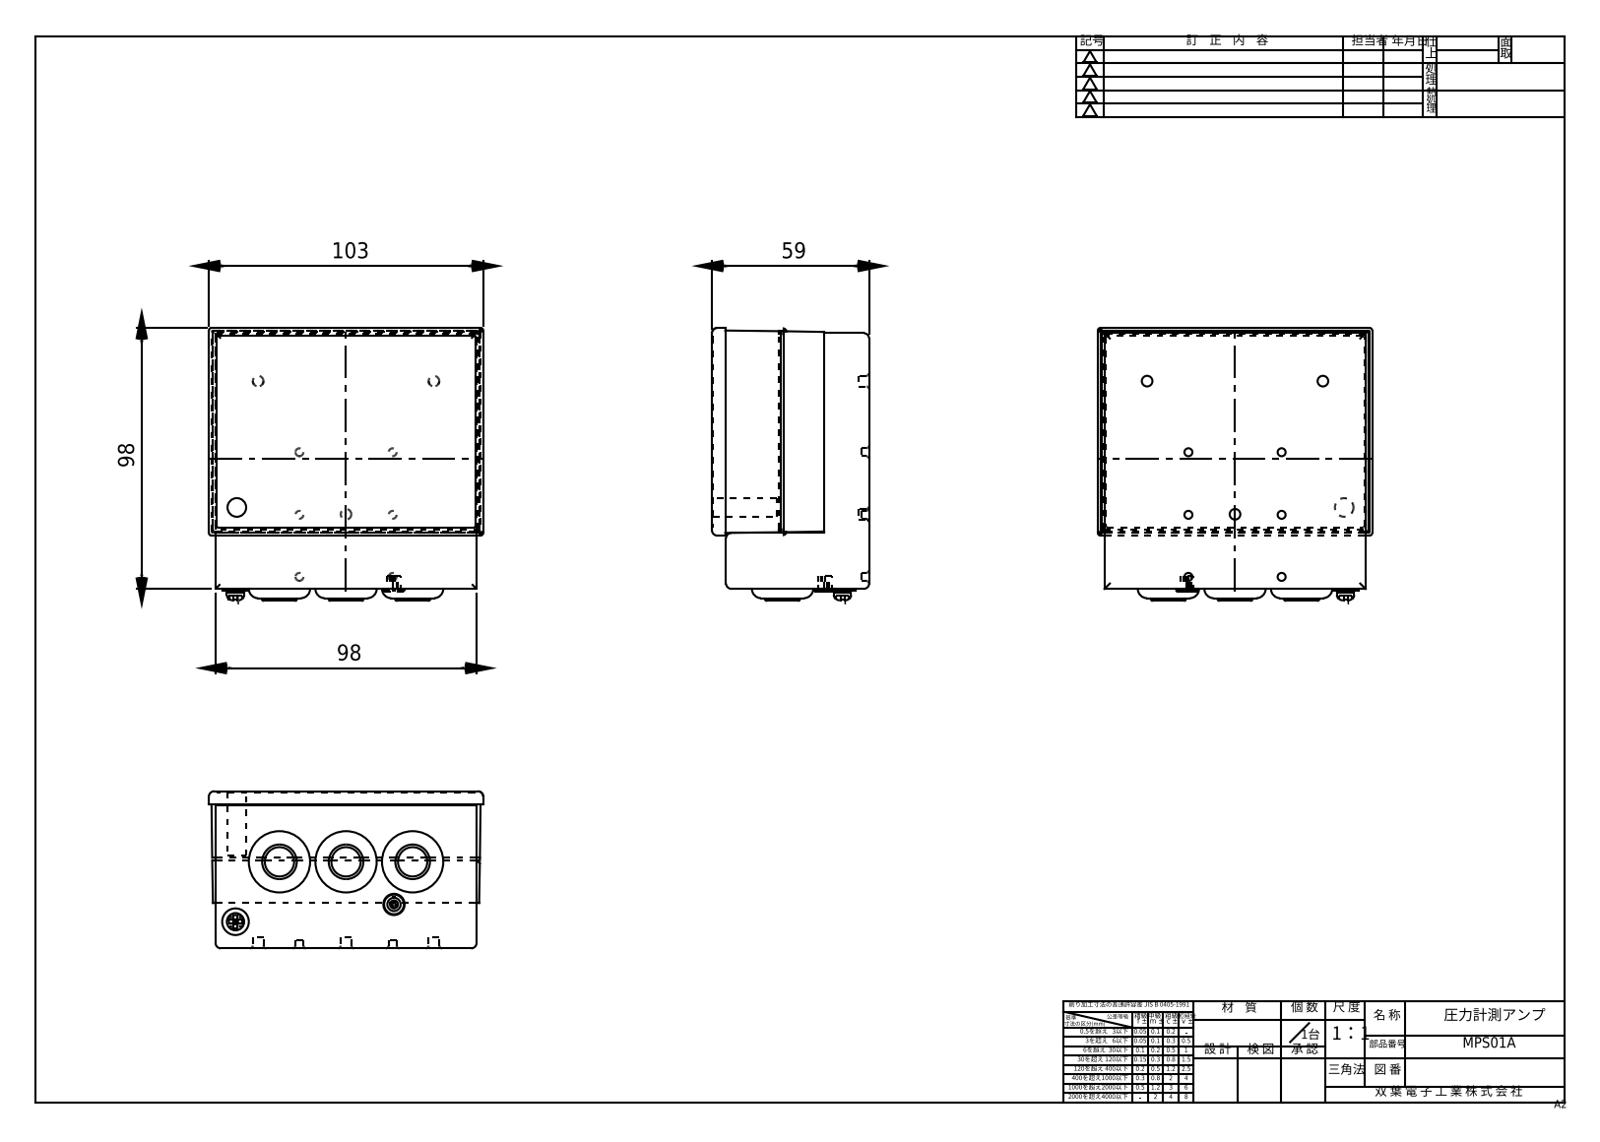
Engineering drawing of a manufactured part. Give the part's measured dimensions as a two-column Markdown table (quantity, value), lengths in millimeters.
| quantity | value |
| --- | --- |
| STEP written by | XStep 1.0 (automotive_design) |
| units | millimeters |
| bodies | 1 solid, 152 faces (70 planar, 60 cylindrical, 22 other) |
| overall size | 103 × 102.5 × 59 |
| volume | 556 036 mm³ |
| surface area | 51 935 mm² |
| round holes (diameter × count) | 3 × 6, 0.6 × 3, 4 × 3, 11 × 3, 5 × 1, 7 × 1 |
| round bosses / shafts (diameter × count) | 13 × 3, 10 × 1, 8 × 1, 6.5 × 1, 6 × 1, 3 × 1 |
| partial cylindrical surfaces (radius × count) | 0.5 × 16, 2 × 10, 1 × 4, 2.5 × 1, 2.75 × 1 |
| main face-to-face distances | 58.7, 21, 98, 5, 53.7, 75, 96, 1, 20, 3.5 |
| hole center spacings | 0.8, 1.38, 35, 17.5, 23.3, 23.5, 25, 29.14 |
